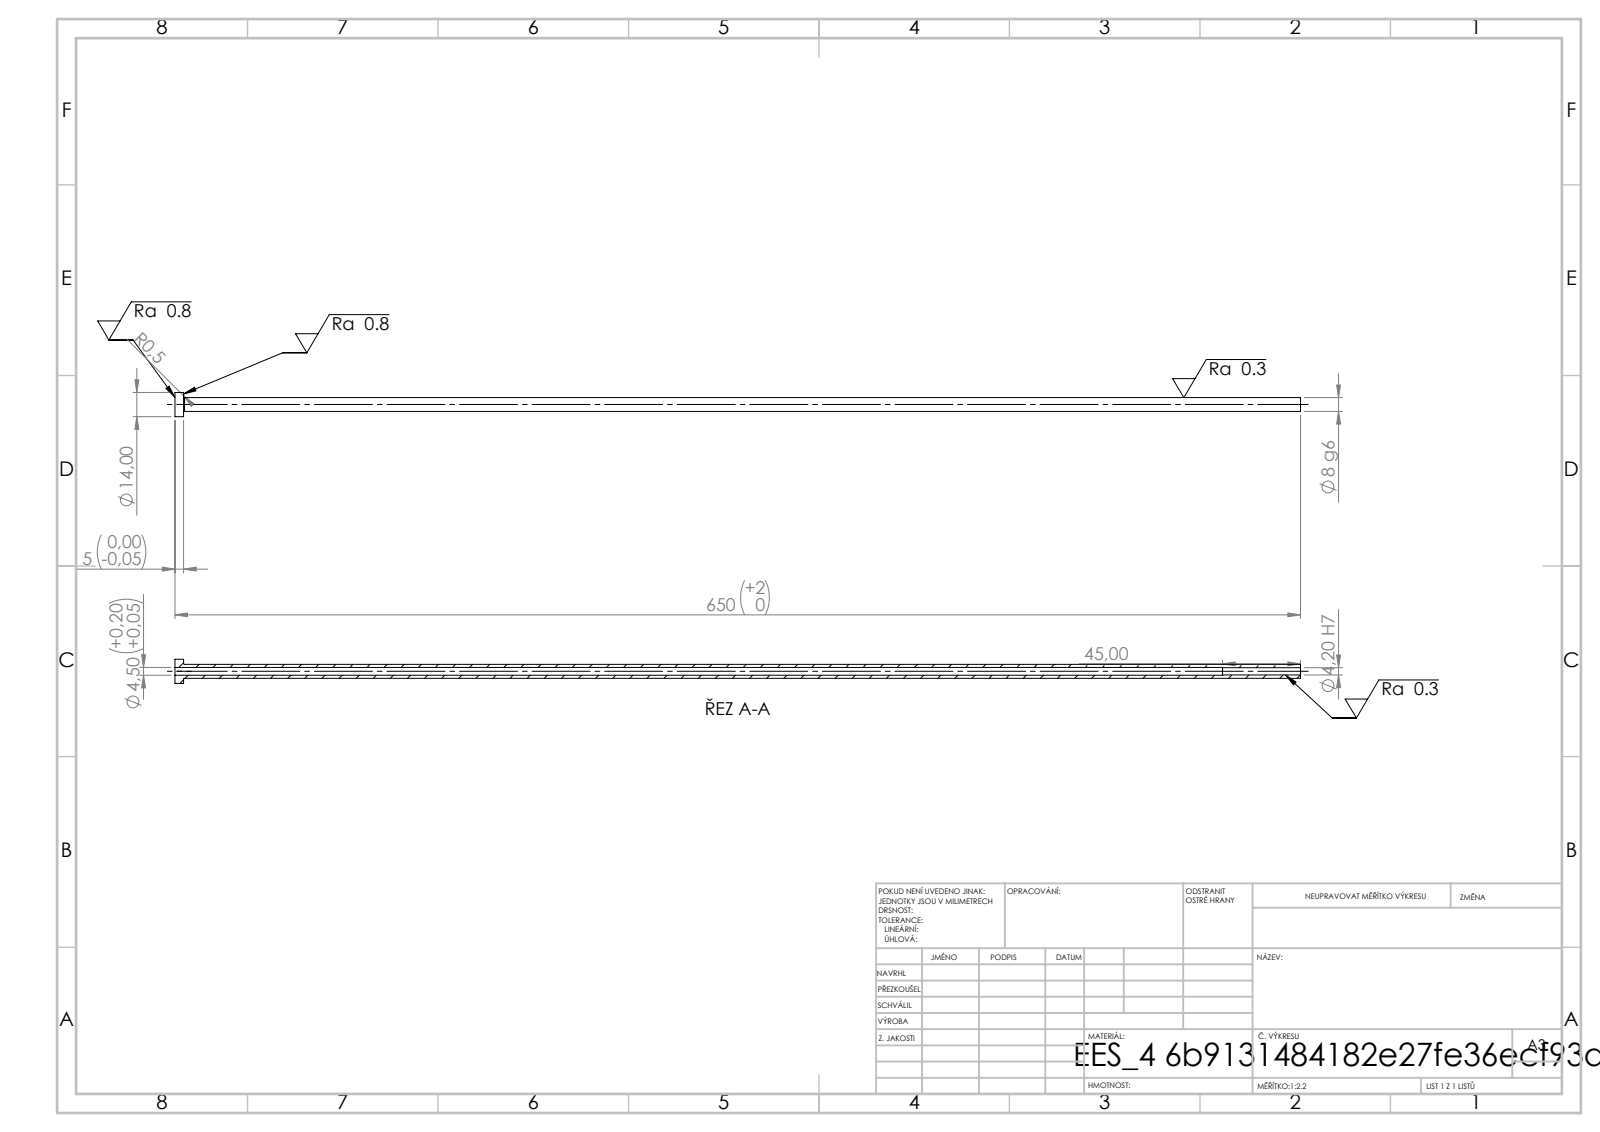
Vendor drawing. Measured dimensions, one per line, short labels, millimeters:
written by: SolidWorks 2019 (CONFIG_CONTROL_DESIGN)
unit: mm
bodies: 1 solid, 14 faces (4 planar, 8 cylindrical, 2 other)
size: 650 × 14 × 14
volume: 22 947 mm³; area: 25 852 mm²
holes: 1× ⌀4.2, 1× ⌀4.5
bosses: 1× ⌀14, 1× ⌀8
face distances: 5, 650, 645, 605, 600, 45
